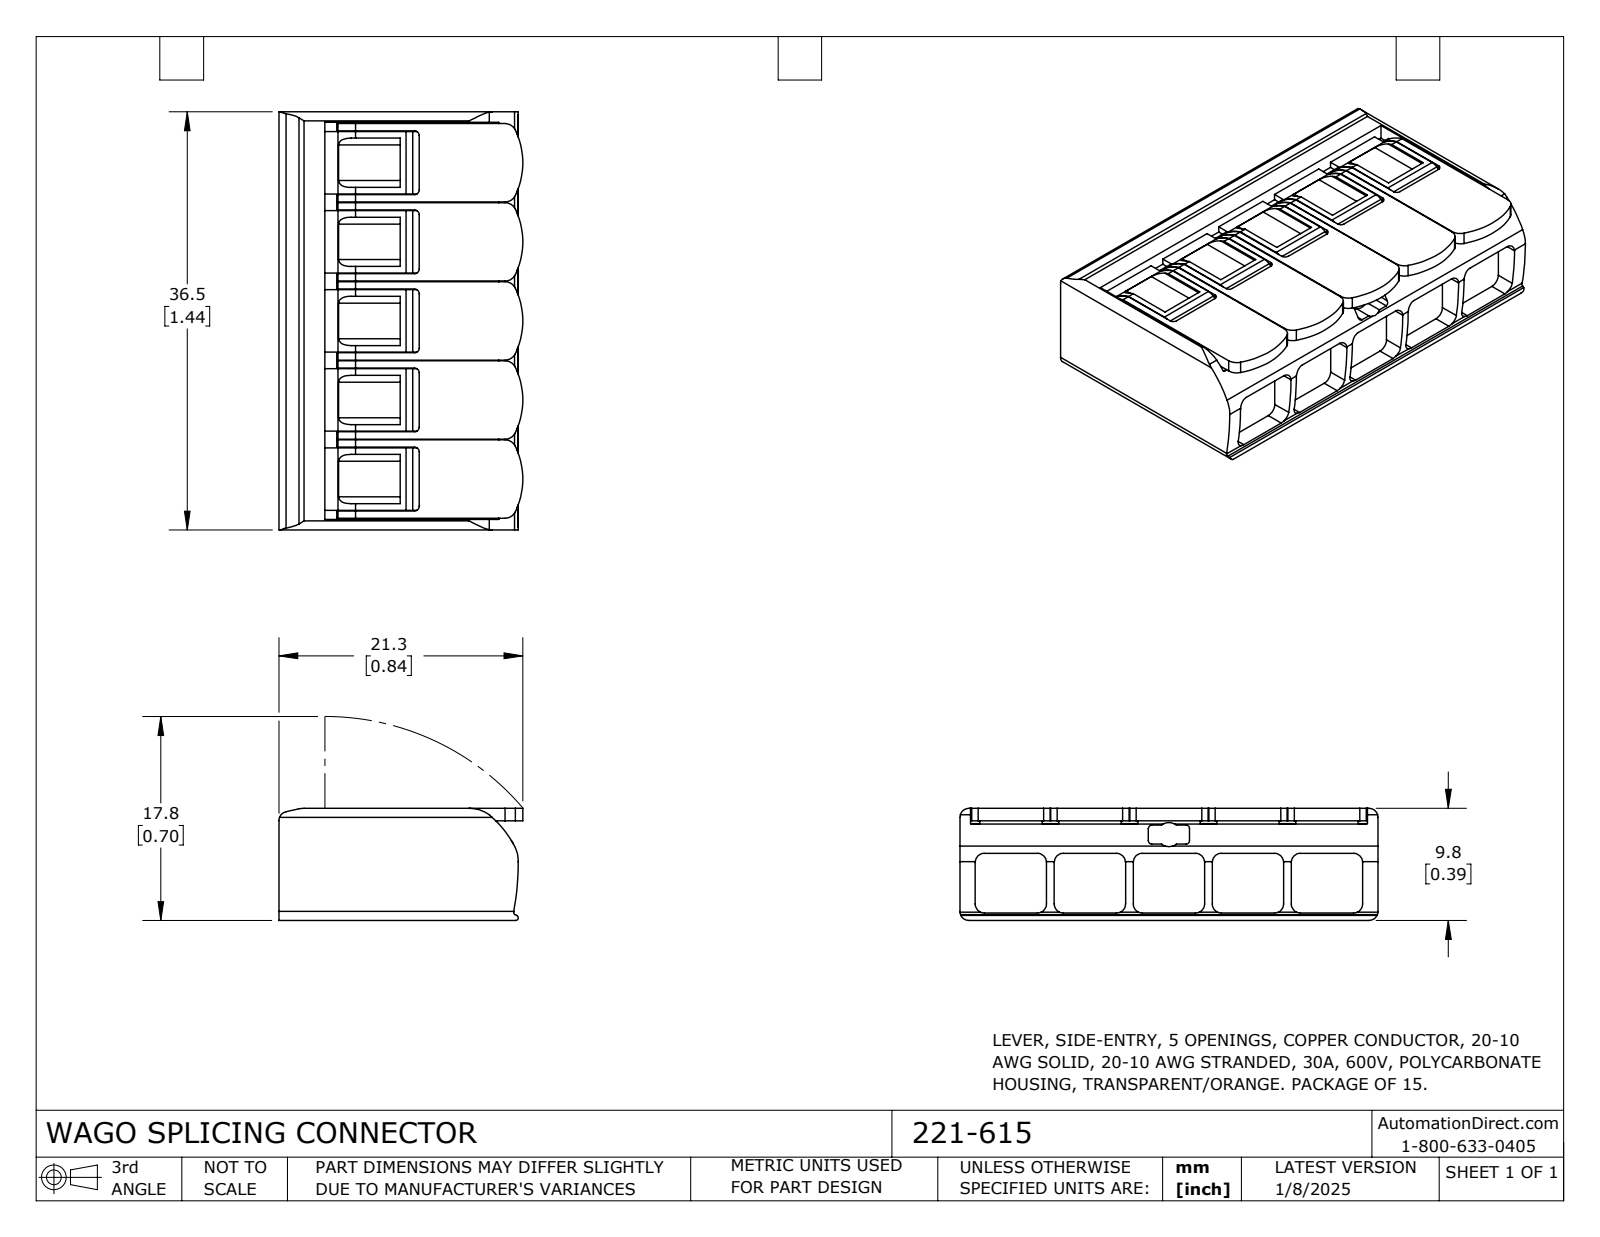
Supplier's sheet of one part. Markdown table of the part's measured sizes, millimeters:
| quantity | value |
| --- | --- |
| part name | 221-615 |
| STEP written by | SolidWorks 2023 (CONFIG_CONTROL_DESIGN) |
| units | millimeters |
| bodies | 1 solid, 251 faces (150 planar, 101 cylindrical, 0 other) |
| overall size | 36.5 × 21.3 × 9.8 |
| volume | 6 850 mm³ |
| surface area | 3 549 mm² |
| partial cylindrical surfaces (radius × count) | 0.8 × 25, 1 × 11, 0.4 × 10, 0.6 × 10, 6.5 × 5, 0.3 × 4, 0.2 × 1, 0.23 × 1 |
| main face-to-face distances | 9.8, 36.5, 18.9, 8.7, 1.1, 6.9, 8.45, 1.35, 0.75, 13.8 |
